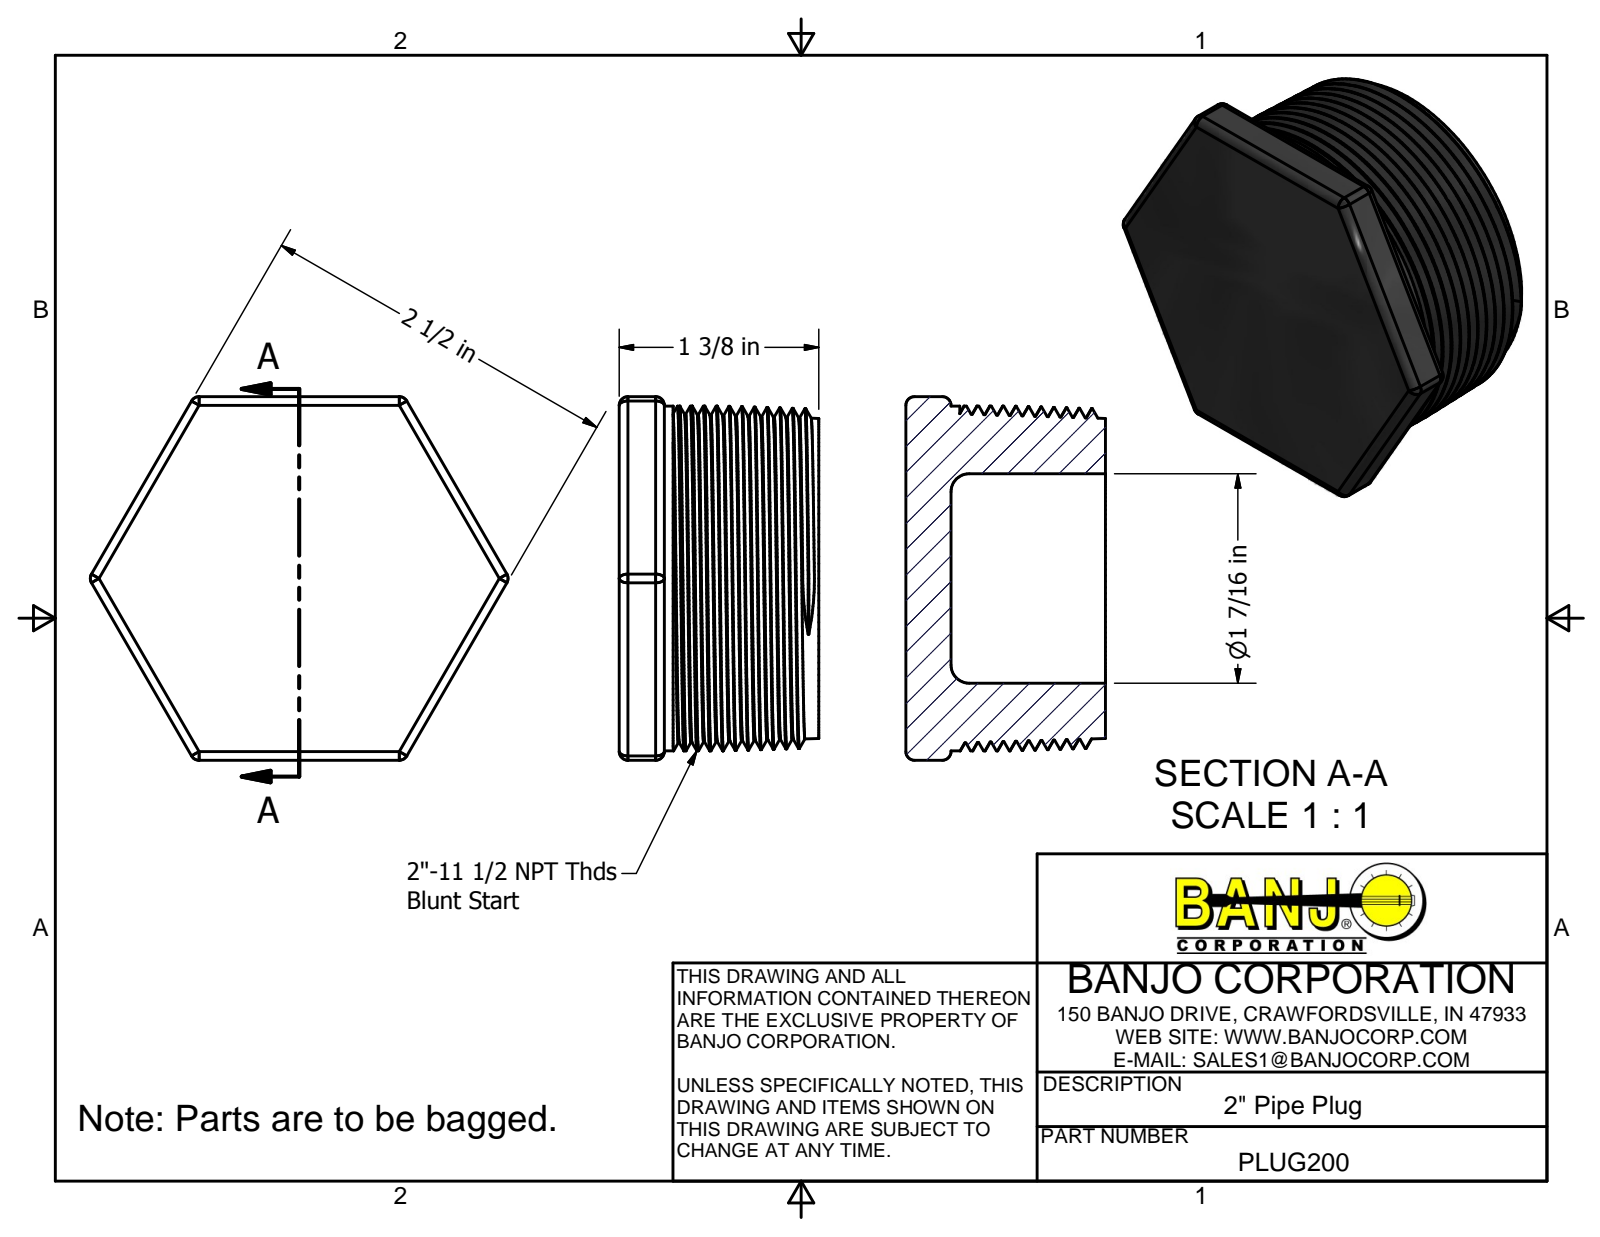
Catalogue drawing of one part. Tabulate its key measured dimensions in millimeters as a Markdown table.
| quantity | value |
| --- | --- |
| part name | PLUG200 |
| STEP written by | Autodesk Inventor 2014 (AUTOMOTIVE_DESIGN) |
| units | millimeters |
| bodies | 1 solid, 68 faces (11 planar, 25 cylindrical, 32 other) |
| overall size | 72.85 × 63.5 × 34.8 |
| volume | 71 056 mm³ |
| surface area | 19 616 mm² |
| round holes (diameter × count) | 36.58 × 1 |
| round bosses / shafts (diameter × count) | 60.2 × 1 |
| partial cylindrical surfaces (radius × count) | 1.52 × 18, 15.66 × 1 |
| main face-to-face distances | 34.79, 26.92, 7.87, 63.5, 25.4, 1.52, 9.39 |
